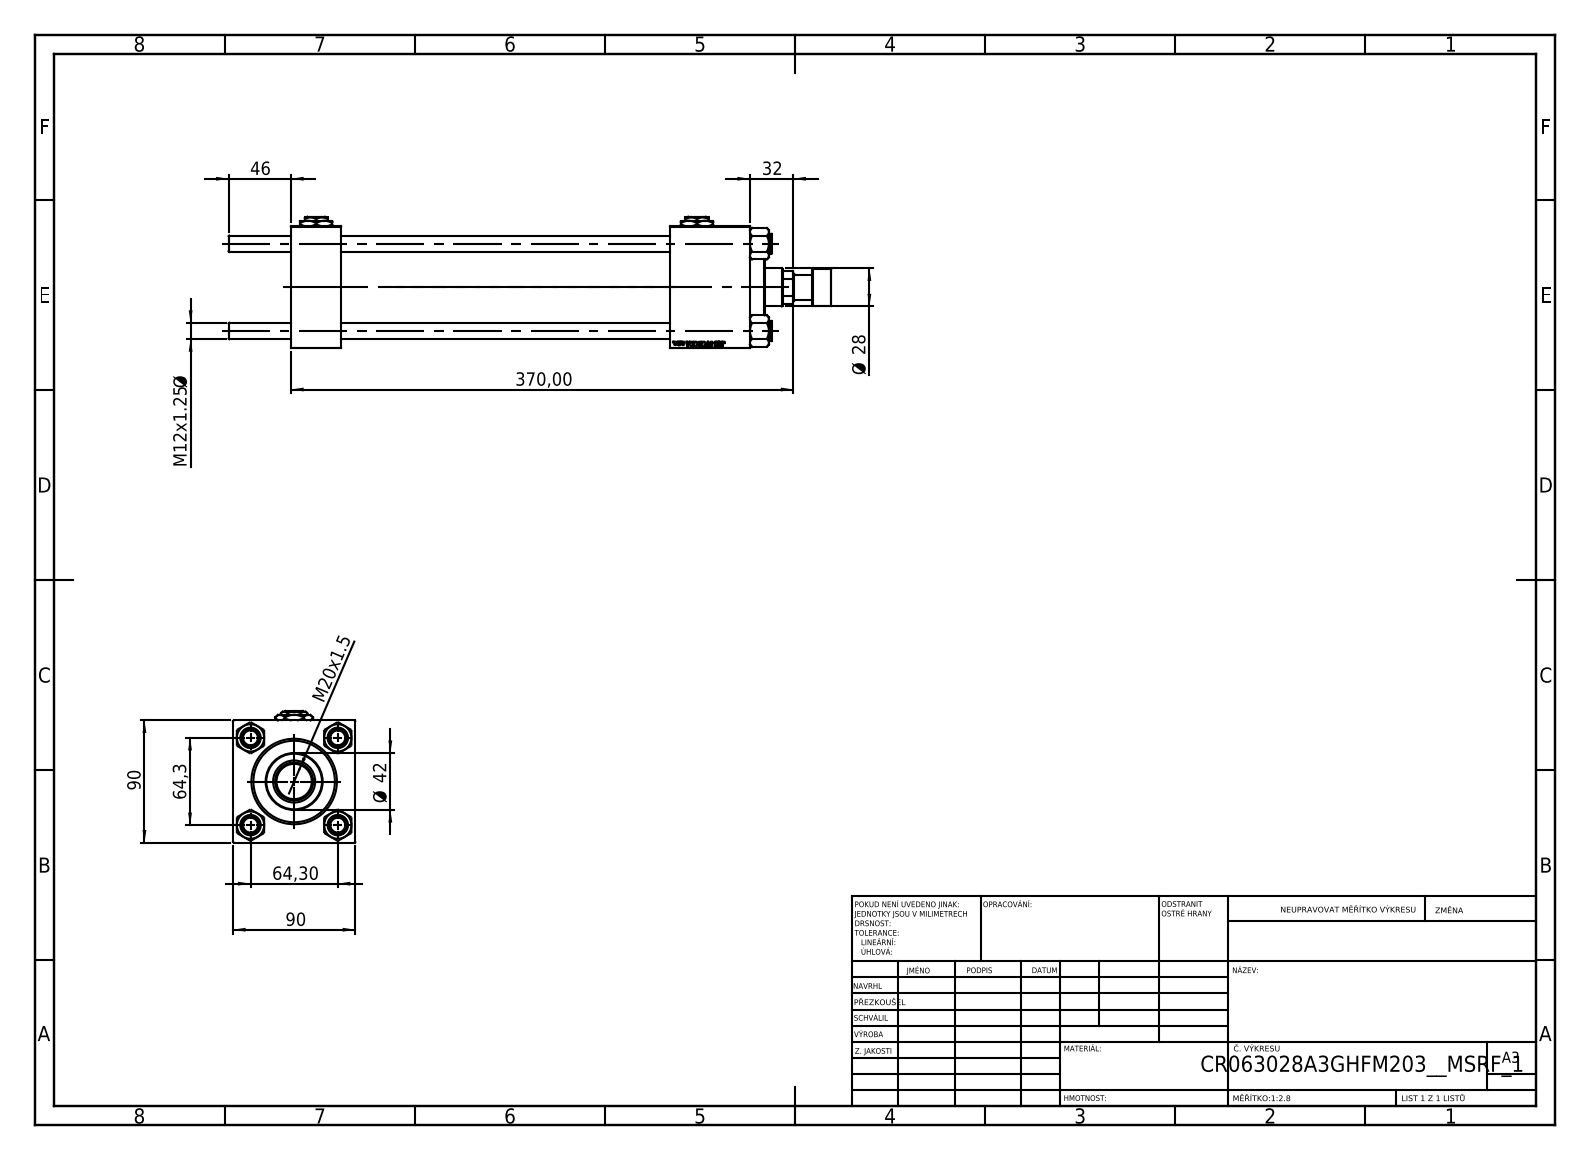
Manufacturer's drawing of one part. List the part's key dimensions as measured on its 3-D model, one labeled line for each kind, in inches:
Part name (STEP PRODUCT): Zatka_pro_OIL_PORT; V215CR_VCP; CR025_012_A_0_G_A_G_M_020_+#_##_TYCINKA; V215_VC_A (+3 more)
STEP written by: SolidWorks 2019 (CONFIG_CONTROL_DESIGN)
Units: inches
Bodies: 14 solids, 1247 faces (571 planar, 92 cylindrical, 584 other)
Overall size (bounding box): 17.48 × 3.819 × 3.543
Volume: 79.09 in³ · Surface area: 500.5 in²
Round holes (diameter × count): ⌀0.472 ×4, ⌀0.276 ×2, ⌀0.825 ×2, ⌀1.181 ×2, ⌀0.728 ×1, ⌀1.102 ×1, ⌀1.22 ×1, ⌀1.969 ×1, ⌀2.362 ×1, ⌀2.48 ×1
Round bosses / shafts (diameter × count): ⌀0.591 ×4, ⌀2.717 ×1, ⌀1.654 ×1, ⌀1.063 ×1, ⌀0.709 ×1
Main face-to-face distances: 3.543, 1.457, 13.307, 11.85, 2.323, 10.984, 9.528, 12.177, 10.72, 1.193
Hole centre spacings: 1.79, 2.531, 3.58, 11.043
